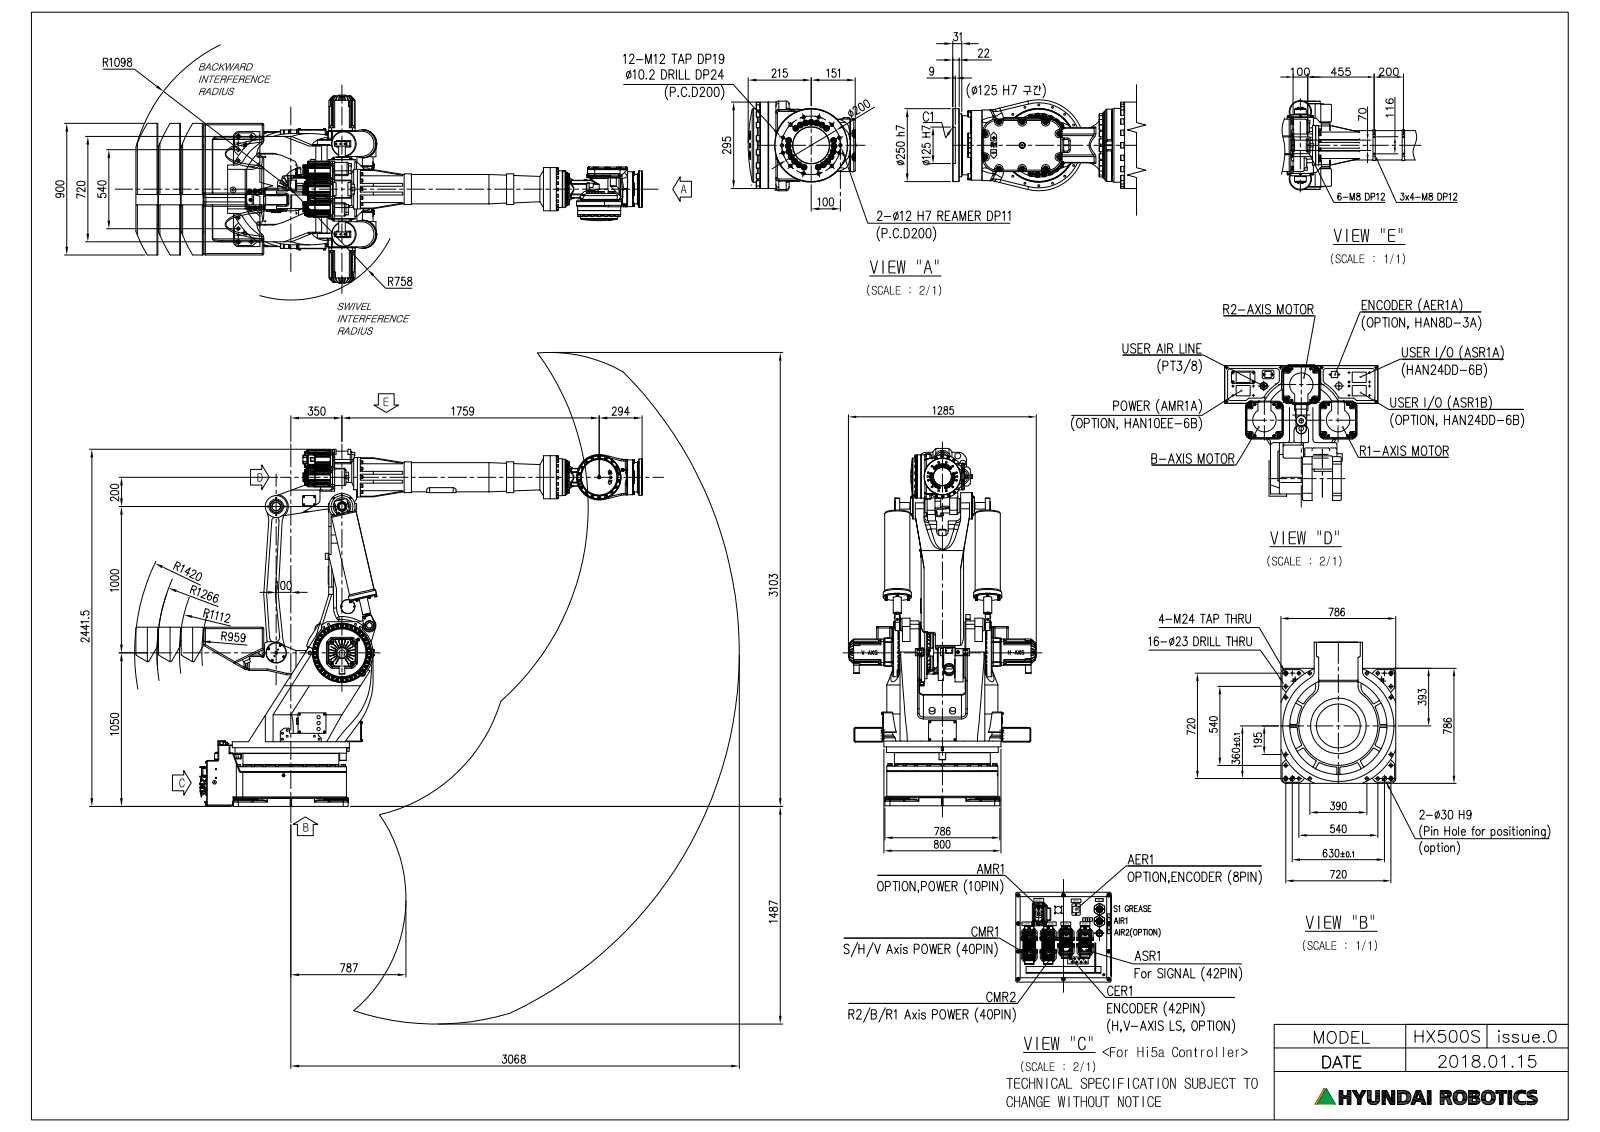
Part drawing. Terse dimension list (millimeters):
name: HX500S_HINGE ASSY; HX500S_A2 FRAME ASSY; [HX500] Mechanical Interface_00; HX500S_R2 Output ASSY (+8 more)
written by: SolidWorks 2017 (AUTOMOTIVE_DESIGN)
unit: mm
bodies: 111 solids, 8704 faces (3450 planar, 3516 cylindrical, 1738 other)
size: 3463 × 2439.5 × 1285
volume: 628 500 000 mm³; area: 27 560 000 mm²
holes: 29× ⌀13, 26× ⌀12, 24× ⌀10.2, 24× ⌀12.5, 18× ⌀9, 16× ⌀8, 13× ⌀10, 12× ⌀7, 8× ⌀6.6, 8× ⌀18, 7× ⌀6, 5× ⌀8.5
bosses: 24× ⌀16, 12× ⌀8.5, 12× ⌀6, 11× ⌀40, 8× ⌀10.22, 7× ⌀30, 5× ⌀100, 5× ⌀50
rounds: 624× R0.2, 220× R10, 128× R8, 126× R5, 57× R60, 54× R1, 48× R0.5, 23× R30
face distances: 5, 155, 310, 987, 10, 15, 1225, 238, 938, 49
hole spacings: 365, 620, 279.36, 674.43, 697.6, 723.75, 152.42, 88
